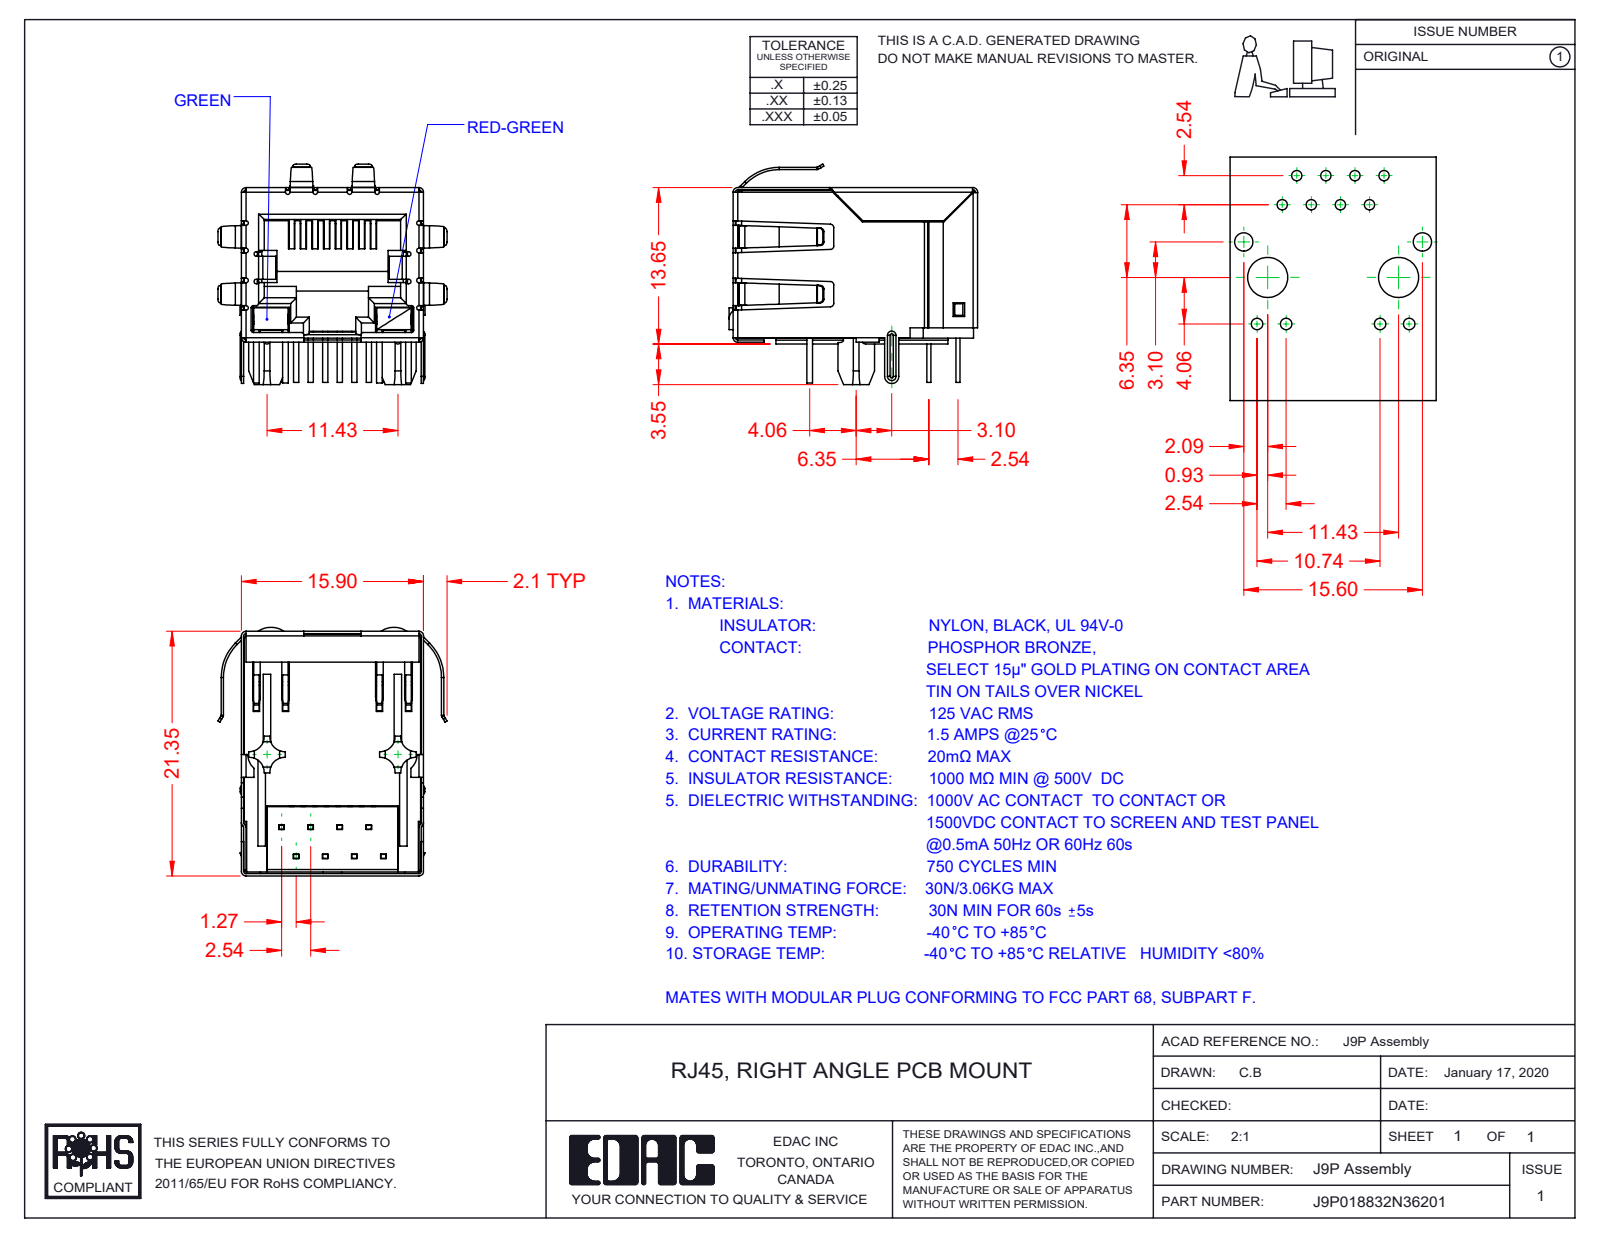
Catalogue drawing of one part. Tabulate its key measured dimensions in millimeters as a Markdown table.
| quantity | value |
| --- | --- |
| part name | 9P-LED Insulator; 9P-LED Contacts; 9P-LED Contact Lock; 9P-LED Shield (+4 more) |
| STEP written by | SolidWorks 2016 (CONFIG_CONTROL_DESIGN) |
| units | millimeters |
| bodies | 13 solids, 1474 faces (1042 planar, 338 cylindrical, 94 other) |
| overall size | 21.7 × 20 × 19.25 |
| volume | 2 687 mm³ |
| surface area | 7 515 mm² |
| partial cylindrical surfaces (radius × count) | 0.2 × 39, 0.5 × 22, 0.3 × 20, 0.4 × 16, 1.3 × 8, 0.23 × 5, 0.11 × 4, 0.31 × 4 |
| main face-to-face distances | 15.45, 15.7, 15.65, 0.35, 0.54, 15.5, 12.36, 0.6, 1.4, 0.59 |
